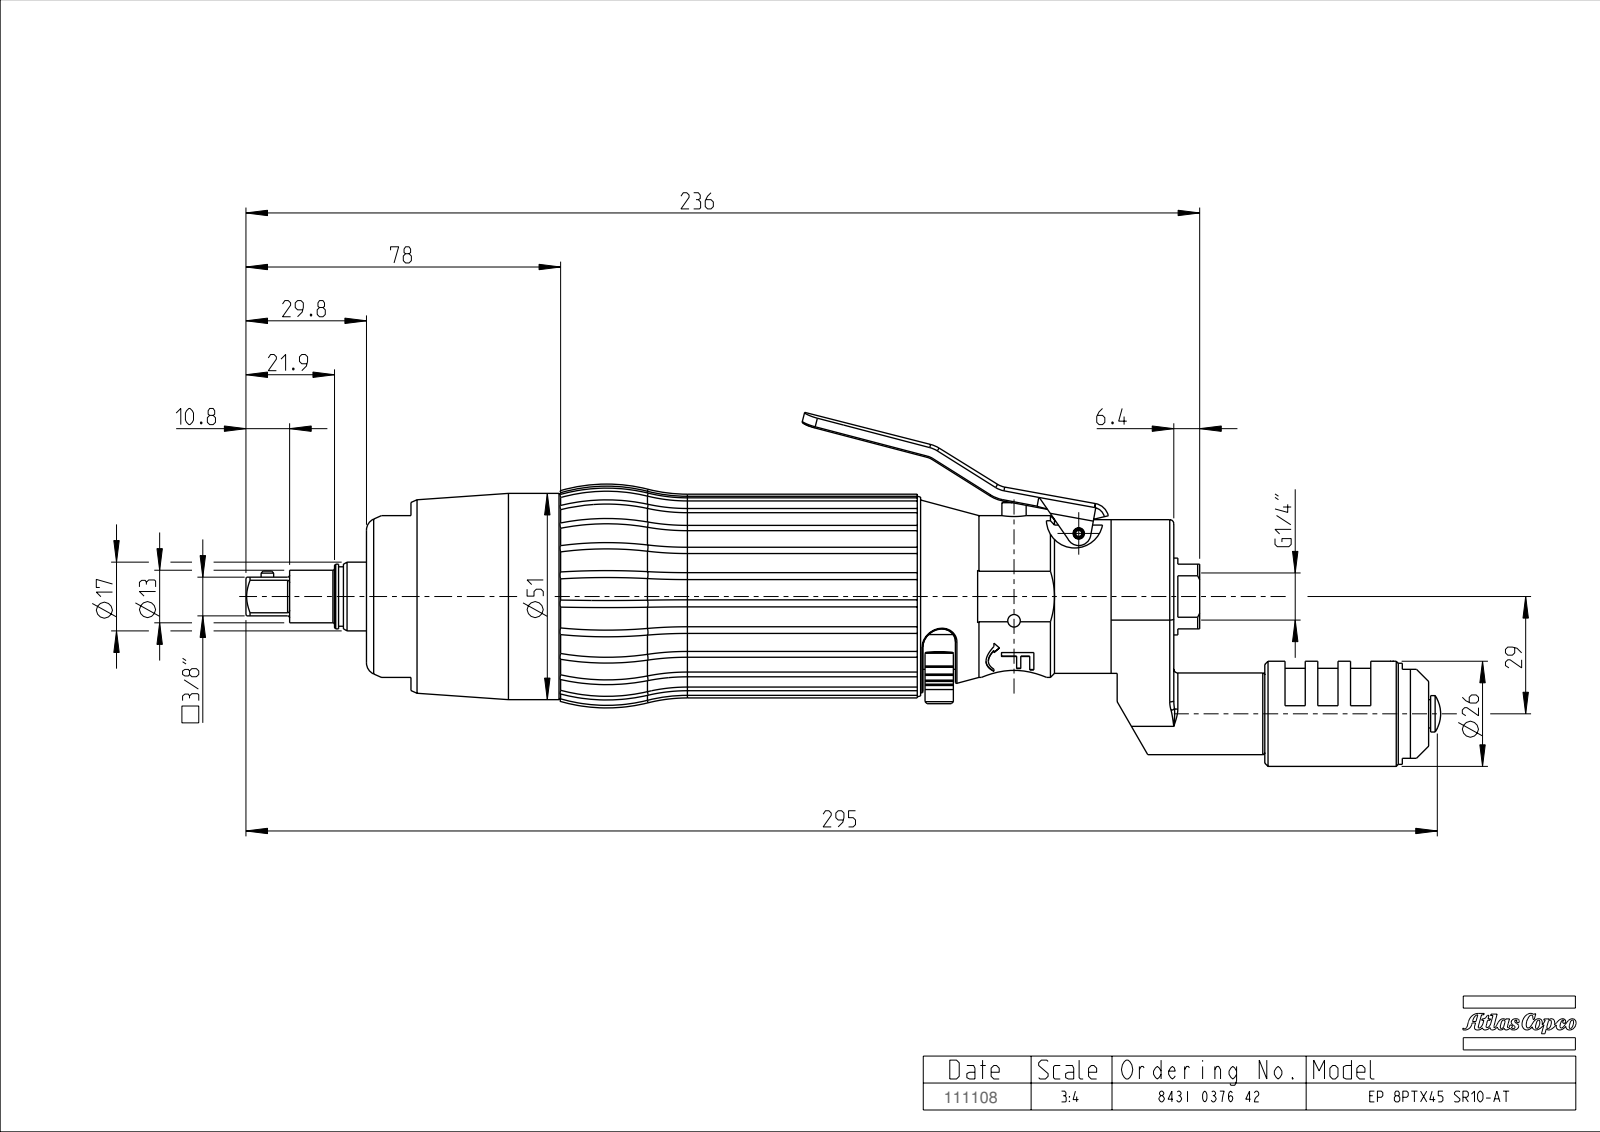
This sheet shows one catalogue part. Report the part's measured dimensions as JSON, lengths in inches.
{"part_name": "EXT_COMP_SW0008", "step_written_by": "CREO PARAMETRIC BY PTC INC, 2020281 (CONFIG_CONTROL_DESIGN)", "units": "inches", "bodies": {"solids": 2, "faces": 745, "planar": 200, "cylindrical": 172, "other": 373}, "overall_size": [11.533, 2.873, 2.32], "volume_in3": 23.32, "surface_area_in2": 83.25, "round_holes": [[0.122, 2], [0.059, 1], [0.079, 1], [0.11, 1], [0.185, 1], [0.213, 1], [0.386, 1], [0.459, 1], [0.472, 1], [0.512, 1], [0.61, 1], [0.724, 1]], "round_bosses_or_shafts": [[0.591, 2], [2.008, 1], [1.575, 1], [1.496, 1], [1.024, 1], [0.984, 1], [0.906, 1], [0.795, 1]], "partial_cylinders_radius": [[0.039, 25], [0.012, 8], [0.02, 6], [0.138, 4], [0.079, 3], [0.069, 2], [0.157, 2], [0.118, 1]], "face_to_face_distances": [7.858, 5.417, 1.594, 1.516, 1.457, 1.89, 3.051, 0.039, 1.575, 0.059], "hole_center_spacings": [0.098, 1.058, 1.142, 1.219, 3.968, 4.631, 7.27]}
